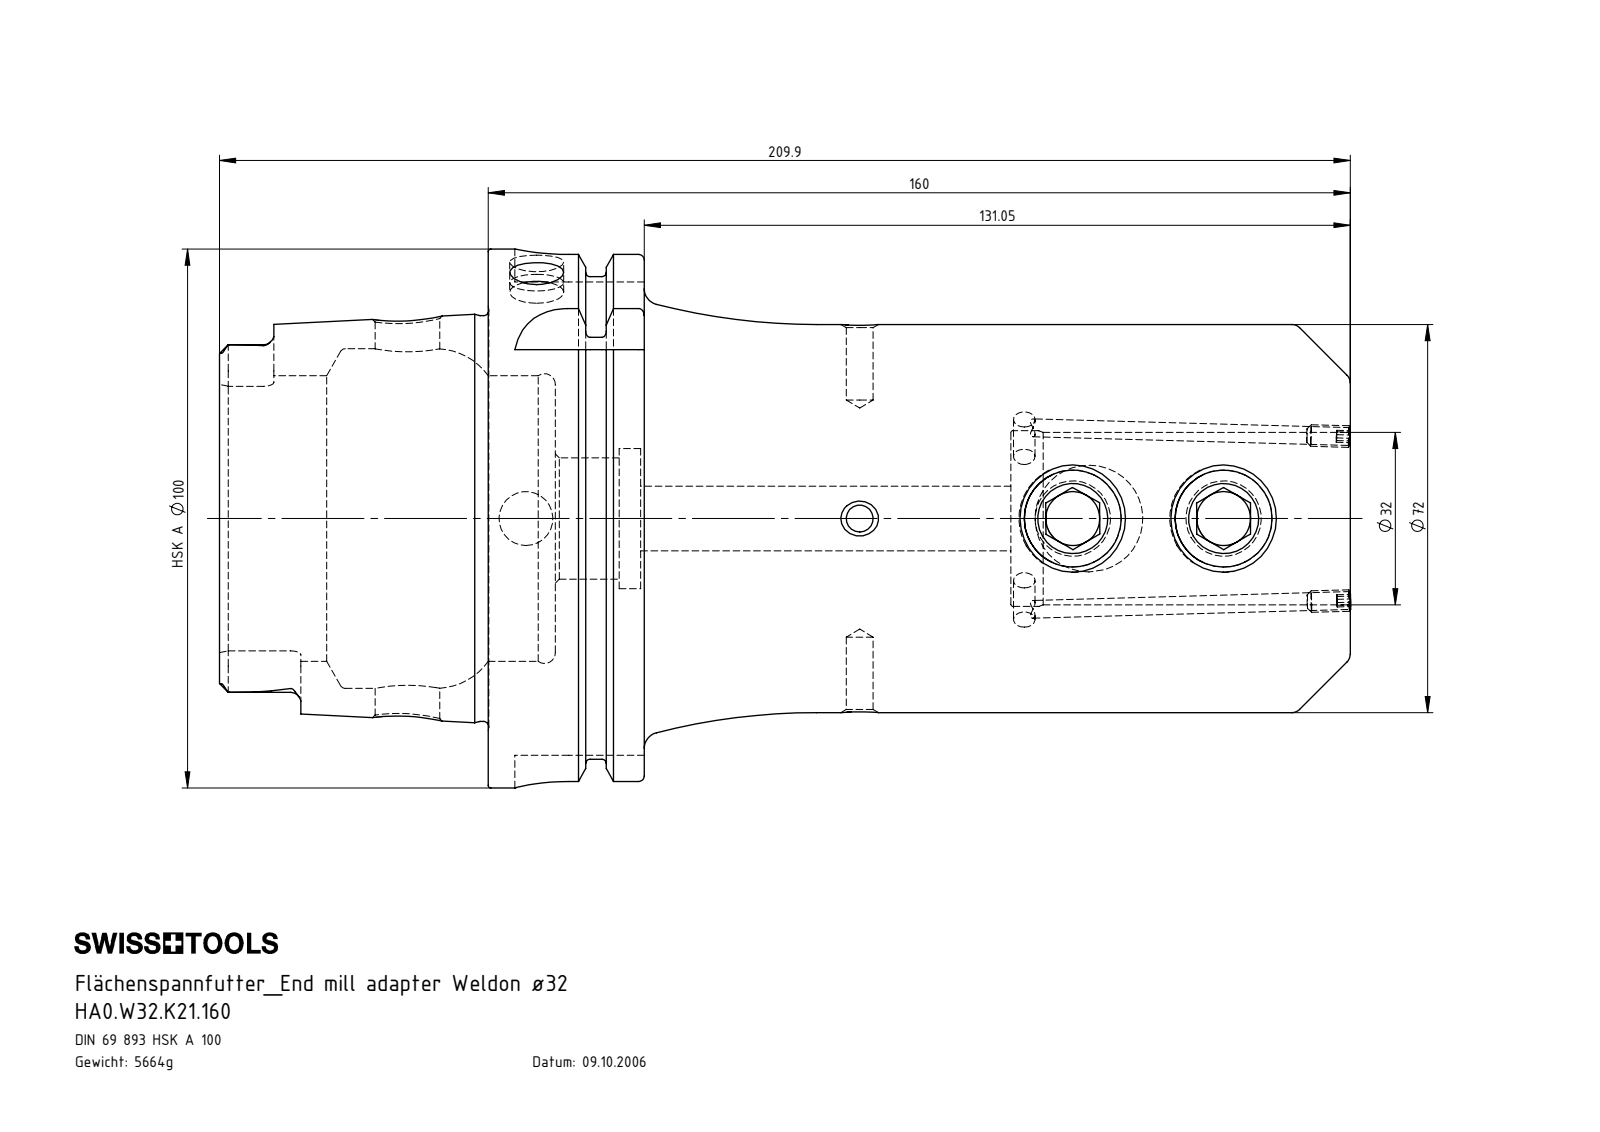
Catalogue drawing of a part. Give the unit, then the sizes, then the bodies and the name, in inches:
Units: inches
Overall size (bounding box): 8.268 × 3.937 × 3.937
Round holes (diameter × count): ⌀0.394 ×3, ⌀0.13 ×2, ⌀0.197 ×2, ⌀0.472 ×2, ⌀0.709 ×2, ⌀0.157 ×1, ⌀0.886 ×1, ⌀1.024 ×1, ⌀1.26 ×1, ⌀1.283 ×1, ⌀2.087 ×1, ⌀2.48 ×1
Round bosses / shafts (diameter × count): ⌀0.787 ×2, ⌀0.157 ×2, ⌀3.937 ×1, ⌀3.62 ×1, ⌀2.963 ×1, ⌀2.835 ×1
Partial cylindrical surfaces — rounded edges, fillets, slot ends (radius × count): R0.075 ×6, R0.192 ×4, R0.394 ×4
Main face-to-face distances: 1.14, 0.49, 0.65, 6.299, 5.809, 5.159, 1.965, 2.455, 3.104, 8.264
Hole centre spacings: 1.102, 1.557, 2.439, 2.659, 3.305, 3.996, 5.098
Volume: 44.03 in³ · Surface area: 146.8 in²
Bodies: 5 solids, 305 faces (90 planar, 82 cylindrical, 133 other)
Part name (STEP PRODUCT): W32-ER1.001.020_Default; HA0.W32.K21.160; HA0-W32.K21.160_D_Fertigbearbeitung; ERU-CJ3.001.008_Default
STEP written by: SolidWorks 2009 (CONFIG_CONTROL_DESIGN)
